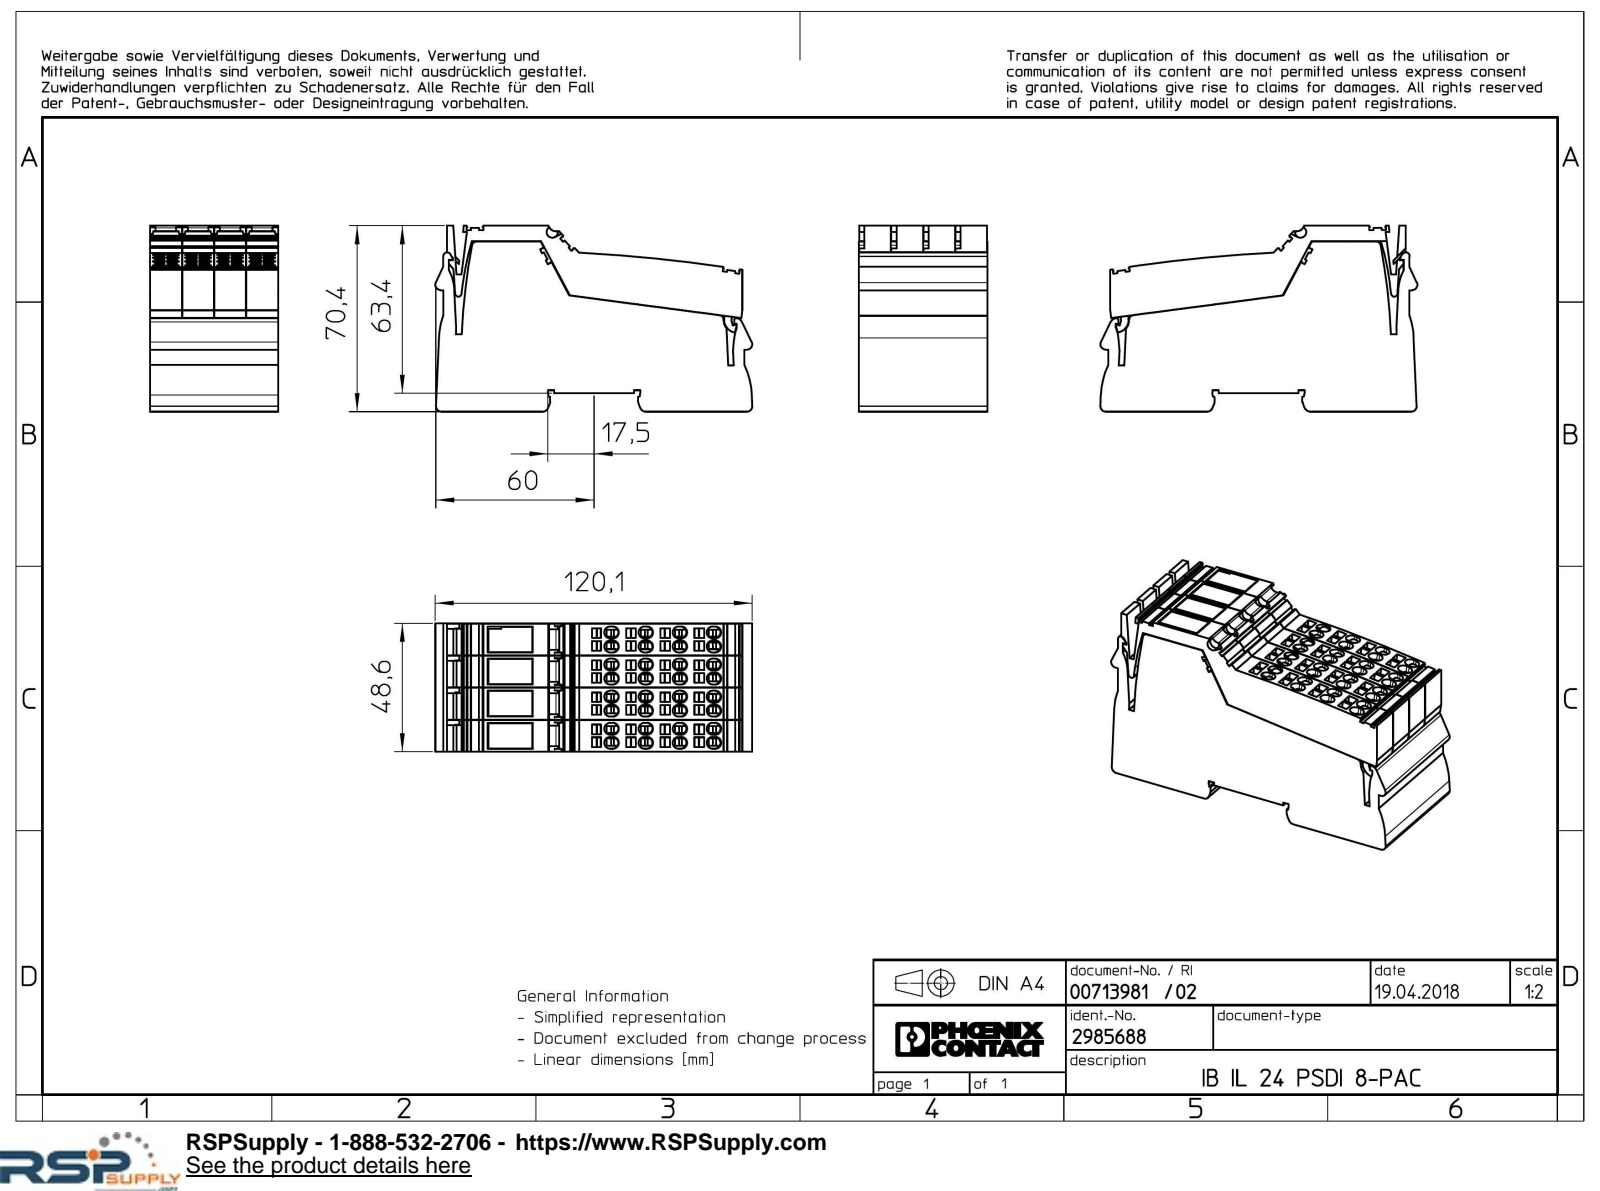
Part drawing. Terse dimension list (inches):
name: L_L_ST_YE_1018-select.4; L_L_8_GEH_YE_1018-select; L_L_LWL_HBU-select.2; L-L_LWL_HBU_AUSSEN-select (+1 more)
written by: Creo Elements/Direct Modeling 20.1A 29-Sep-2018 (C) Parametric Technology GmbH (AUTOMOTIVE_DESIGN)
unit: in
bodies: 9 solids, 2113 faces (1820 planar, 181 cylindrical, 112 other)
size: 4.729 × 2.773 × 1.913
volume: 19.58 in³; area: 126.3 in²
holes: 24× ⌀0.047
rounds: 64× R0.089, 8× R0.024, 6× R0.079, 2× R0.006, 2× R0.067, 2× R0.335, 2× R0.374, 2× R0.657
face distances: 0.478, 0.957, 0.472, 1.913, 0.951, 1.435, 0.484, 1.429, 1.023, 0.511
hole spacings: 0.701, 0.478, 0.512, 0.546, 1.085, 0.189, 0.588, 0.841
